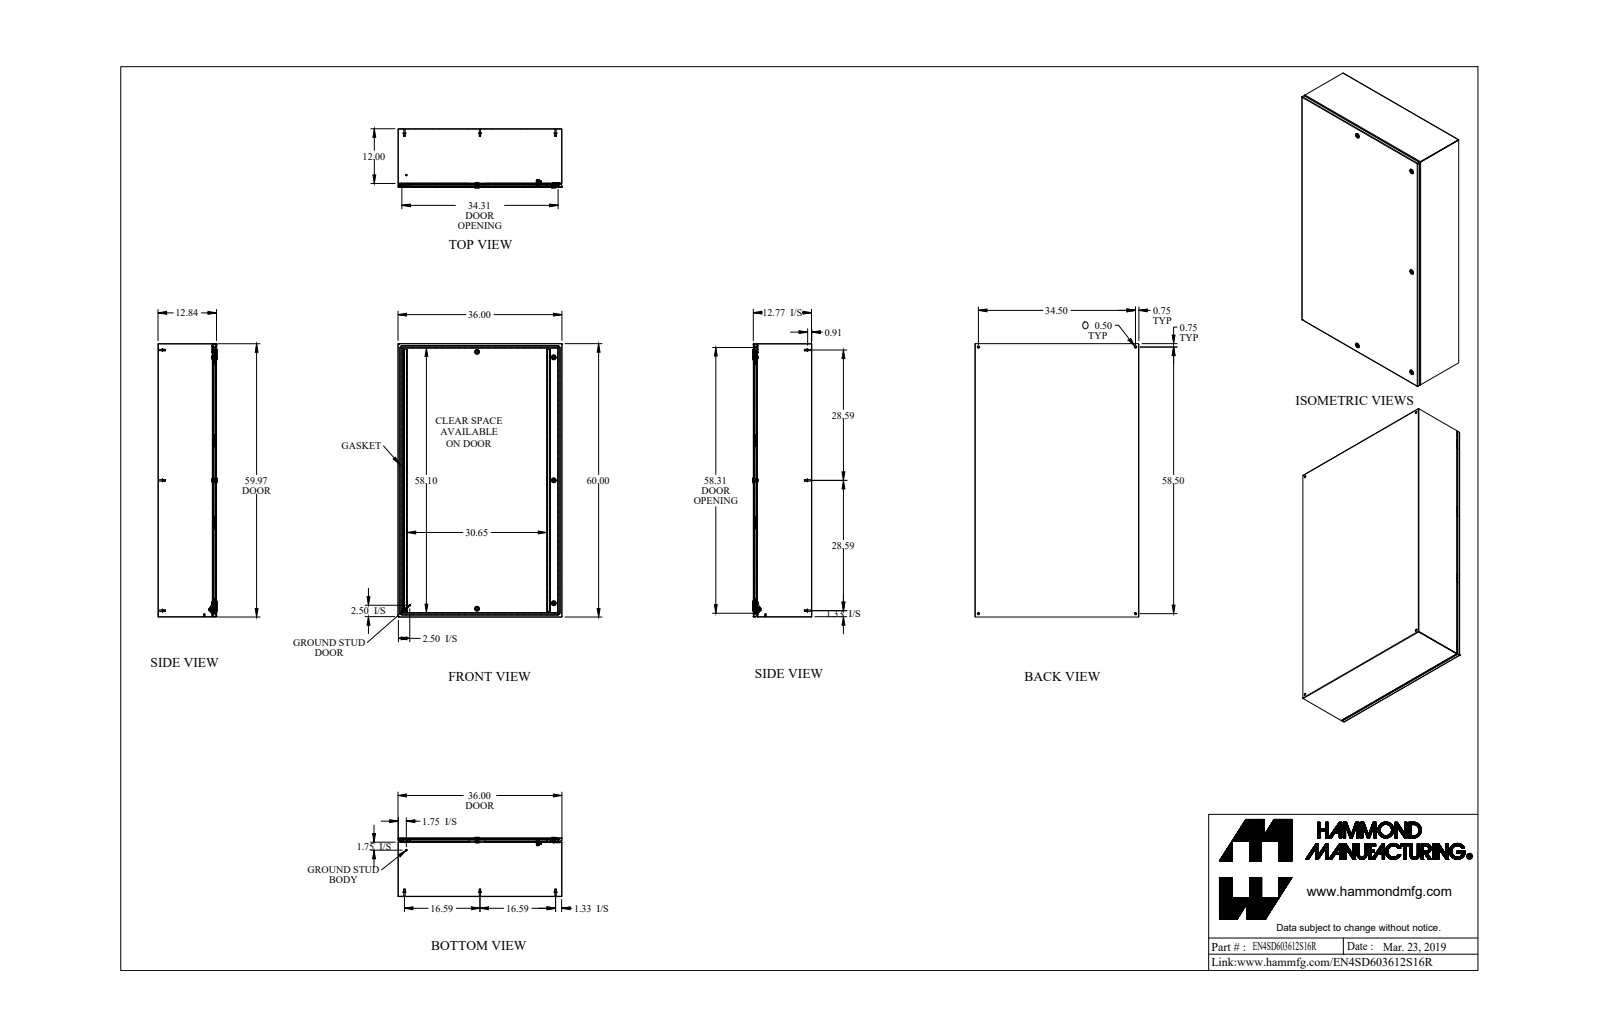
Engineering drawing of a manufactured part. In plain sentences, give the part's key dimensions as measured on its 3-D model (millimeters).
The part is named "EN4SD603612S16R". Its 3-D file was written by "SolidWorks 2018 (AUTOMOTIVE_DESIGN)". It is 66 solids with 1711 faces: 896 planar, 546 cylindrical and 269 other. Overall it measures 1524 by 914.4 by 330.3 millimeters. Its volume is 8 931 000 cubic millimeters and its surface area 9 984 000 square millimeters. Round holes: 9 of diameter 12.7, 5 of diameter 5, 5 of diameter 9.8, 5 of diameter 16, 5 of diameter 19.5, 1 of diameter 4.4, 1 of diameter 5, 1 of diameter 6.1, 1 of diameter 6.1, 1 of diameter 7, 1 of diameter 9.5. Round bosses or shafts: 10 of diameter 8, 9 of diameter 15.9, 8 of diameter 7, 5 of diameter 27.9, 5 of diameter 15.9, 5 of diameter 6, 3 of diameter 19.9, 3 of diameter 13.3. Partial cylindrical surfaces (rounded edges, fillets, slot ends): 24 of radius 1.1, 18 of radius 0.9, 18 of radius 2.7, 17 of radius 1.6, 10 of radius 2.4, 10 of radius 3.2, 9 of radius 0.4, 8 of radius 0.2. The main face-to-face distances are 1.8, 324.4, 322.5, 326.2, 912.6, 910.7, 914.4, 1.8, 1520.3, 1522.2. The hole center spacings are 422.5, 428.8, 455.4, 743.4, 851.3, 876.3, 1128.4, 1465.2.
